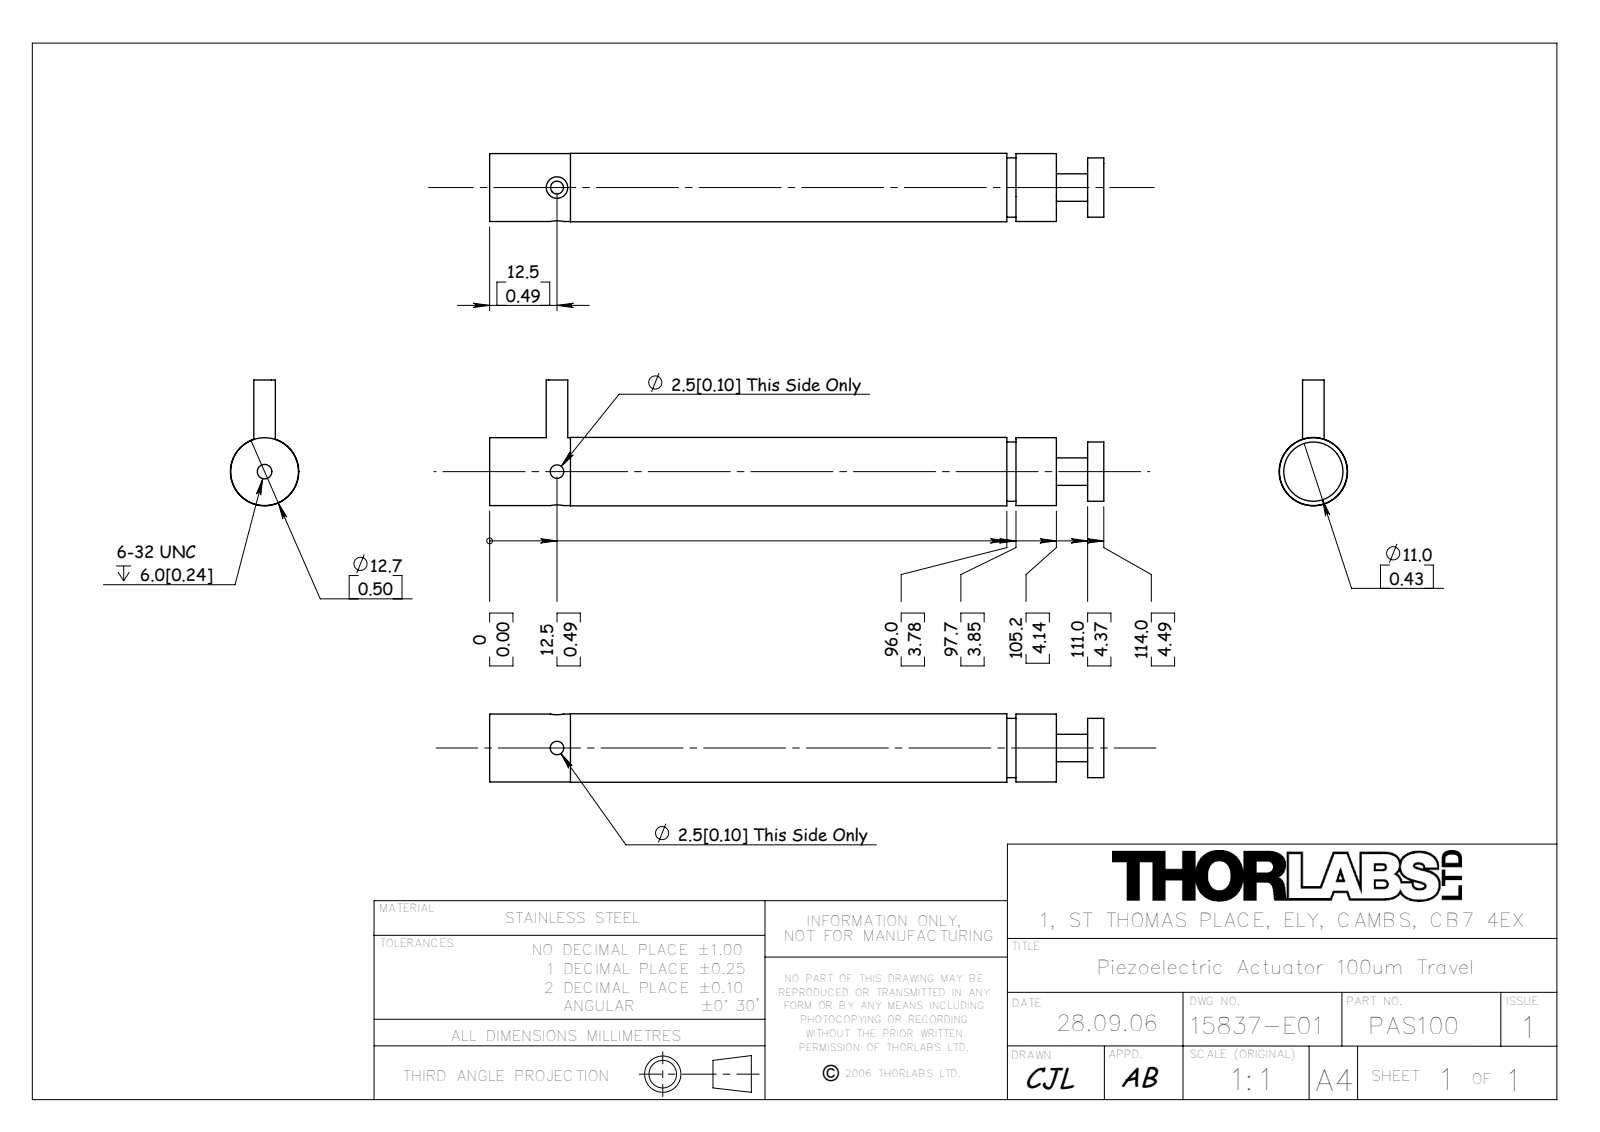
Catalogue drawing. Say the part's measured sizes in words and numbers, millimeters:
The part is named "15837-E0W". Its 3-D file was written by "SolidWorks 2007 (AUTOMOTIVE_DESIGN)". It is 0 solids with 38 faces: 10 planar, 28 cylindrical and 0 other. Overall it measures 114 by 23.35 by 12.7 millimeters. Round holes: 2 of diameter 2.5, 1 of diameter 2.4, 1 of diameter 2.71, 1 of diameter 5.3, 1 of diameter 9.55, 1 of diameter 11.4. Round bosses or shafts: 1 of diameter 12.7, 1 of diameter 12.6, 1 of diameter 11, 1 of diameter 5.1, 1 of diameter 4. The main face-to-face distances are 105.2, 8.8, 114, 3, 5.8, 111, 104, 101, 95.2, 10.
